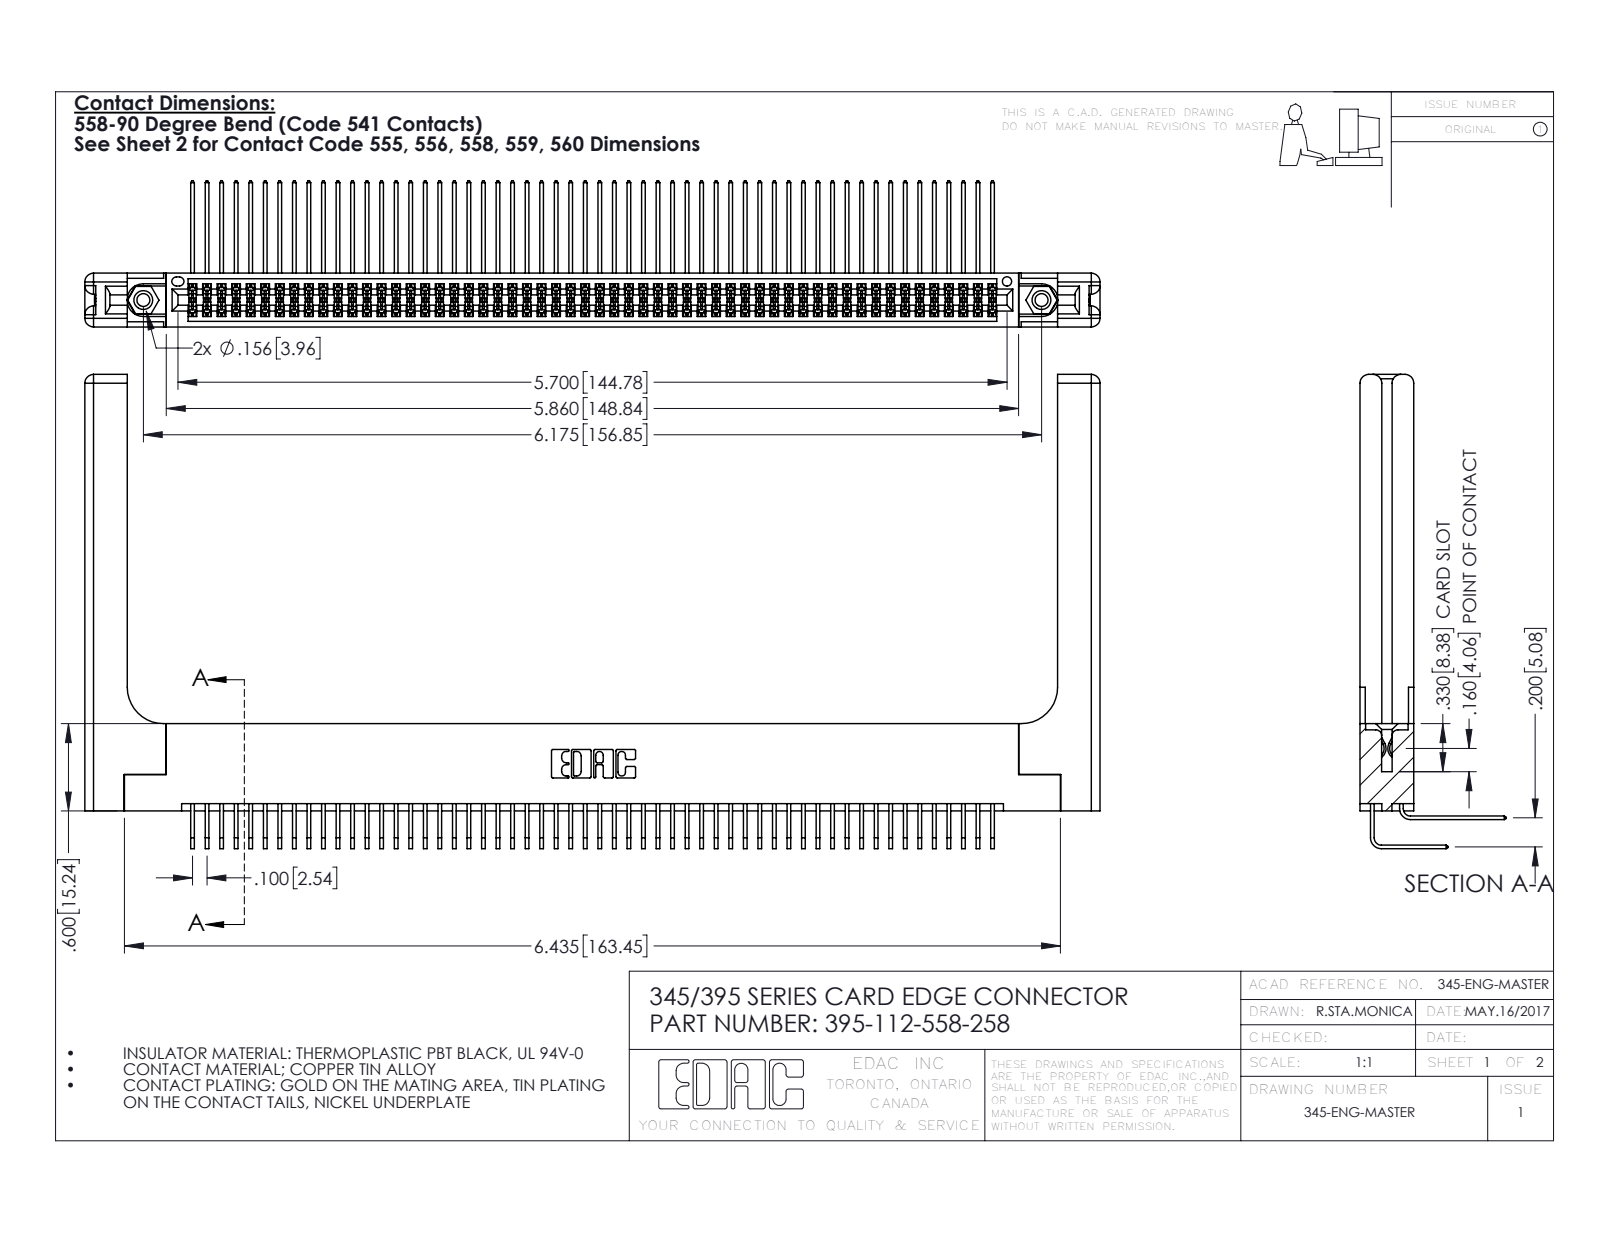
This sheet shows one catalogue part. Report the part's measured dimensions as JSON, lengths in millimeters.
{"part_name": "395-112-558-258; 345-292-001_558 559 Tail - 1; 345-292-001_558 Tail - 2; 345-220-058_345-220-058 (+2 more)", "step_written_by": "SolidWorks 2016 (CONFIG_CONTROL_DESIGN)", "units": "millimeters", "bodies": {"solids": 117, "faces": 6206, "planar": 4148, "cylindrical": 1998, "other": 60}, "overall_size": [177.3, 82.8, 25.5], "volume_mm3": 26470, "surface_area_mm2": 34970, "round_holes": [[2.3, 2], [3.2, 2], [4, 2], [1.6, 1]], "round_bosses_or_shafts": [[3.9, 2]], "partial_cylinders_radius": [[0.2, 169], [0.3, 22], [1.5, 16], [0.2, 6], [0.8, 6], [0.7, 3], [0.4, 2], [0.5, 2]], "face_to_face_distances": [1.8, 7.6, 9.4, 5.1, 2.5, 6.9, 0.6, 5.7, 3.8, 3.8], "hole_center_spacings": [6.9, 150.9, 156.8]}
